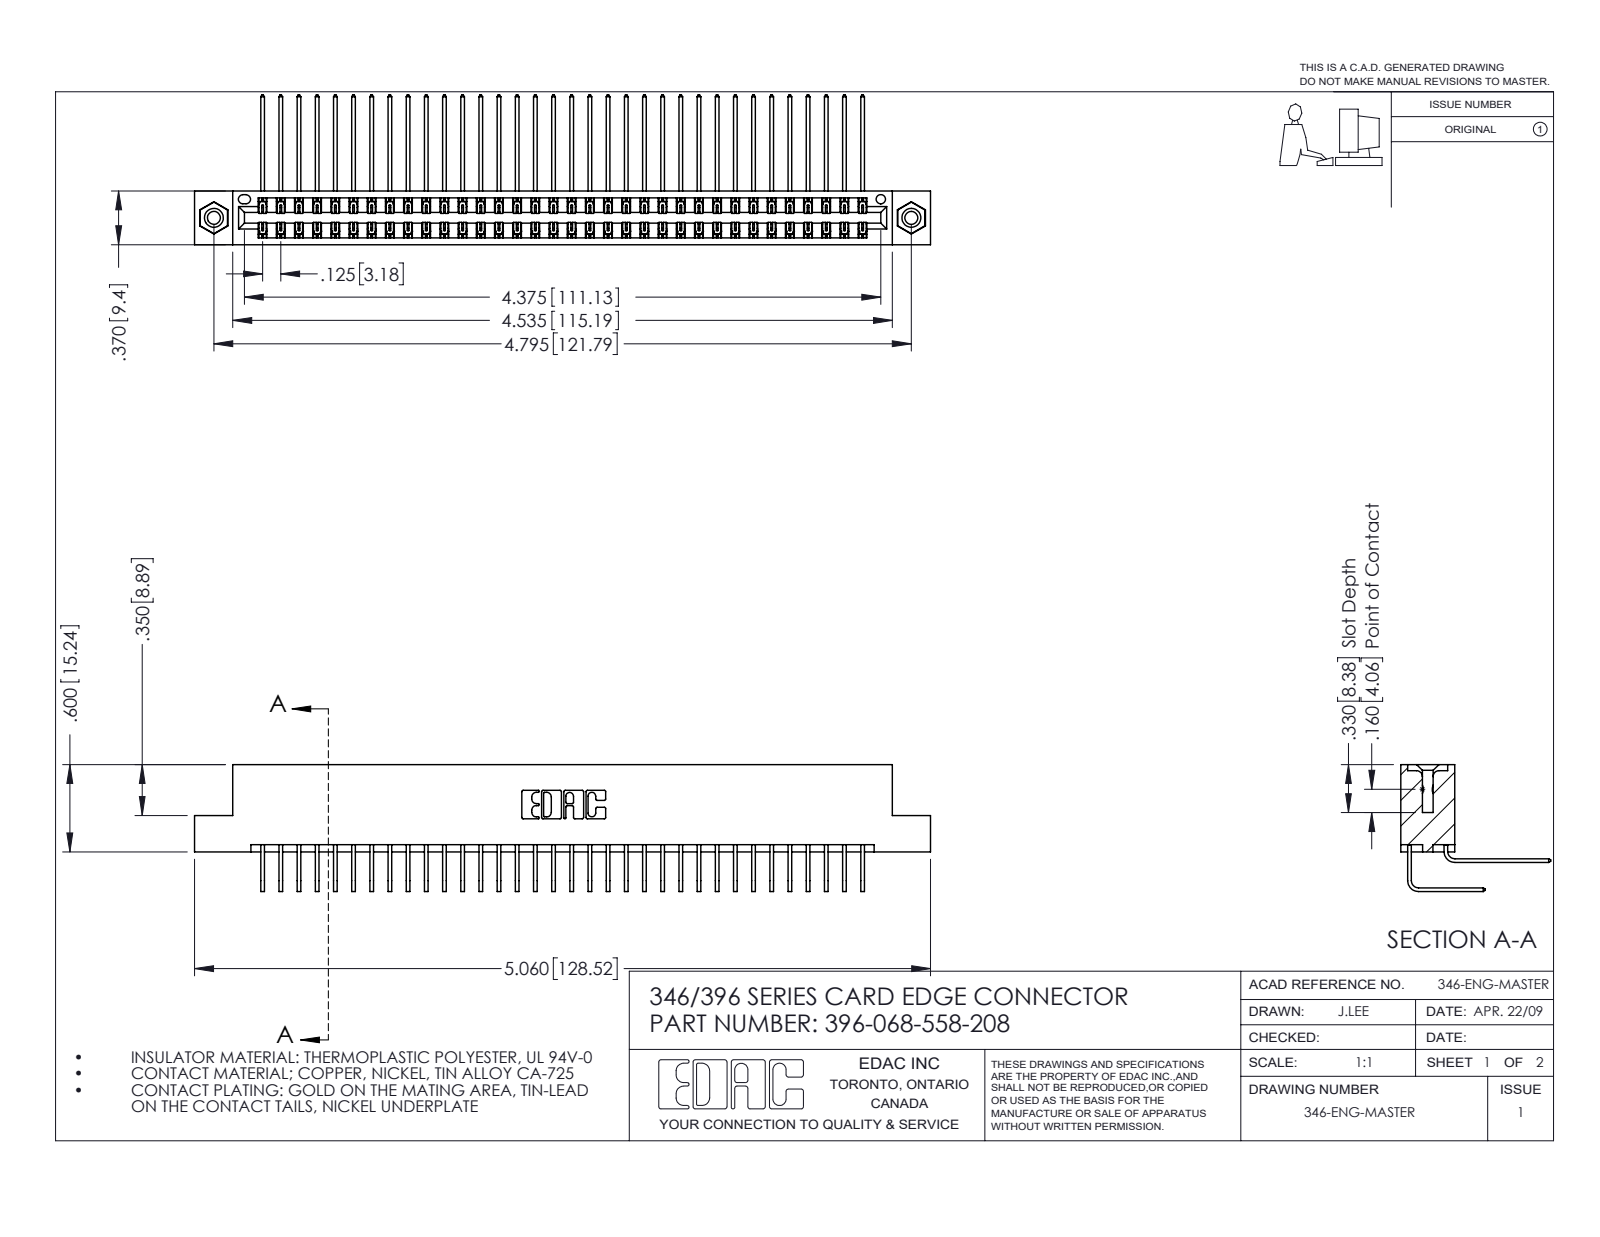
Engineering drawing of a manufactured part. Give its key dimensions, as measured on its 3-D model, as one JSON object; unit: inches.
{"part_name": "396-068-558-208; 346 Part_Flush Mounting Lugs - 0.156 Dia-TI; 345-292-001_558 559 Tail - 1; 345-292-001_558 Tail - 2 (+1 more)", "step_written_by": "SolidWorks 2016 (CONFIG_CONTROL_DESIGN)", "units": "inches", "bodies": {"solids": 71, "faces": 3854, "planar": 2624, "cylindrical": 1214, "other": 16}, "overall_size": [5.06, 1.03, 0.873], "volume_in3": 0.785, "surface_area_in2": 30.14, "round_holes": [[0.089, 2], [0.125, 2], [0.156, 2], [0.064, 1]], "round_bosses_or_shafts": [[0.155, 2]], "partial_cylinders_radius": [[0.006, 102], [0.01, 22], [0.007, 6], [0.031, 6], [0.026, 3], [0.014, 2], [0.022, 2], [0.024, 2]], "face_to_face_distances": [0.048, 0.322, 0.025, 0.25, 0.37, 0.072, 0.298, 0.275, 0.148, 0.222], "hole_center_spacings": [0.246, 4.587, 4.795]}
